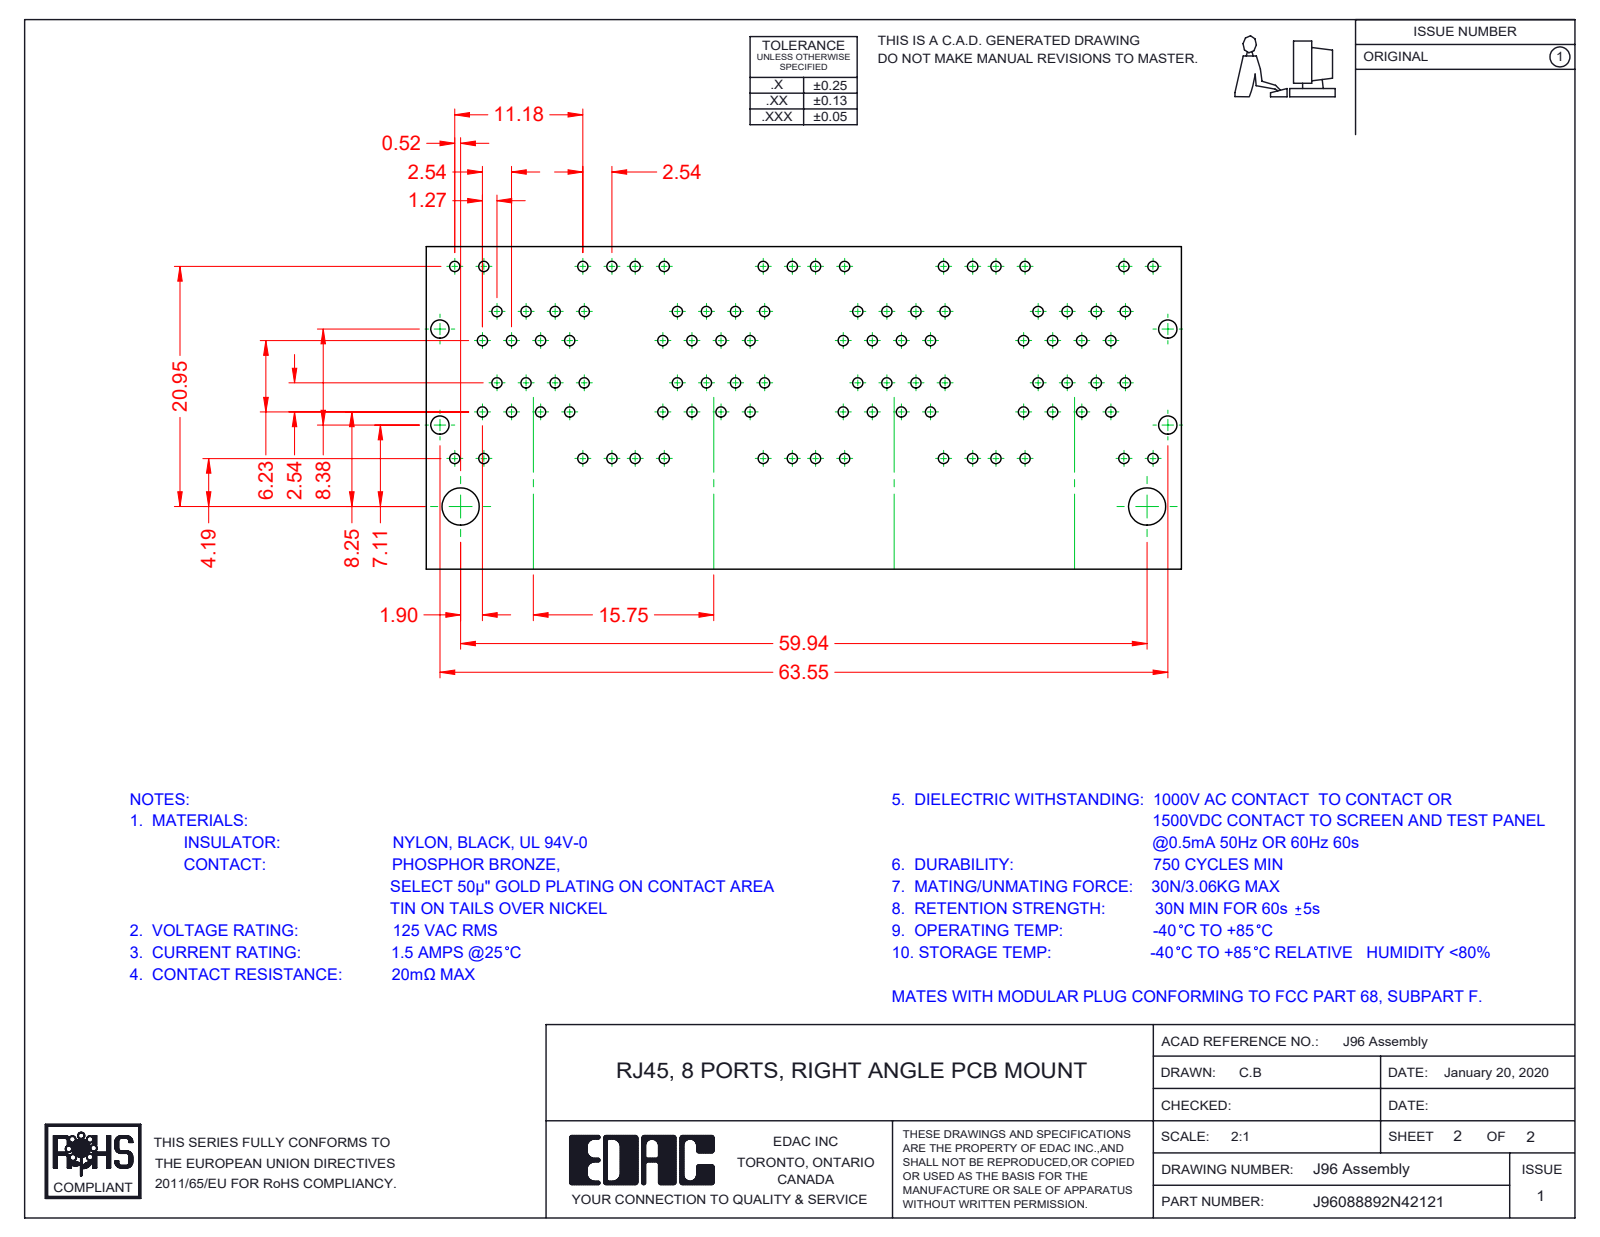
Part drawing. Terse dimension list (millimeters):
name: 96 Grounding_8 Ports; 96 Contact Lock Lower; 96 Contacts Lower; 96 Insulator Insert (+8 more)
written by: SolidWorks 2016 (CONFIG_CONTROL_DESIGN)
unit: mm
bodies: 96 solids, 7642 faces (6069 planar, 1307 cylindrical, 266 other)
size: 64.05 × 29.58 × 28.68
volume: 24 160 mm³; area: 63 658 mm²
holes: 3× ⌀1.7
bosses: 3× ⌀1.68
rounds: 124× R0.25, 73× R0.35, 72× R1, 49× R0.5, 32× R0.91, 21× R0.2, 11× R0.7, 8× R0.22
face distances: 15.75, 0.35, 9.95, 1.17, 1.6, 0.54, 9.98, 10.18, 12.67, 3.37
hole spacings: 15.75, 31.5
